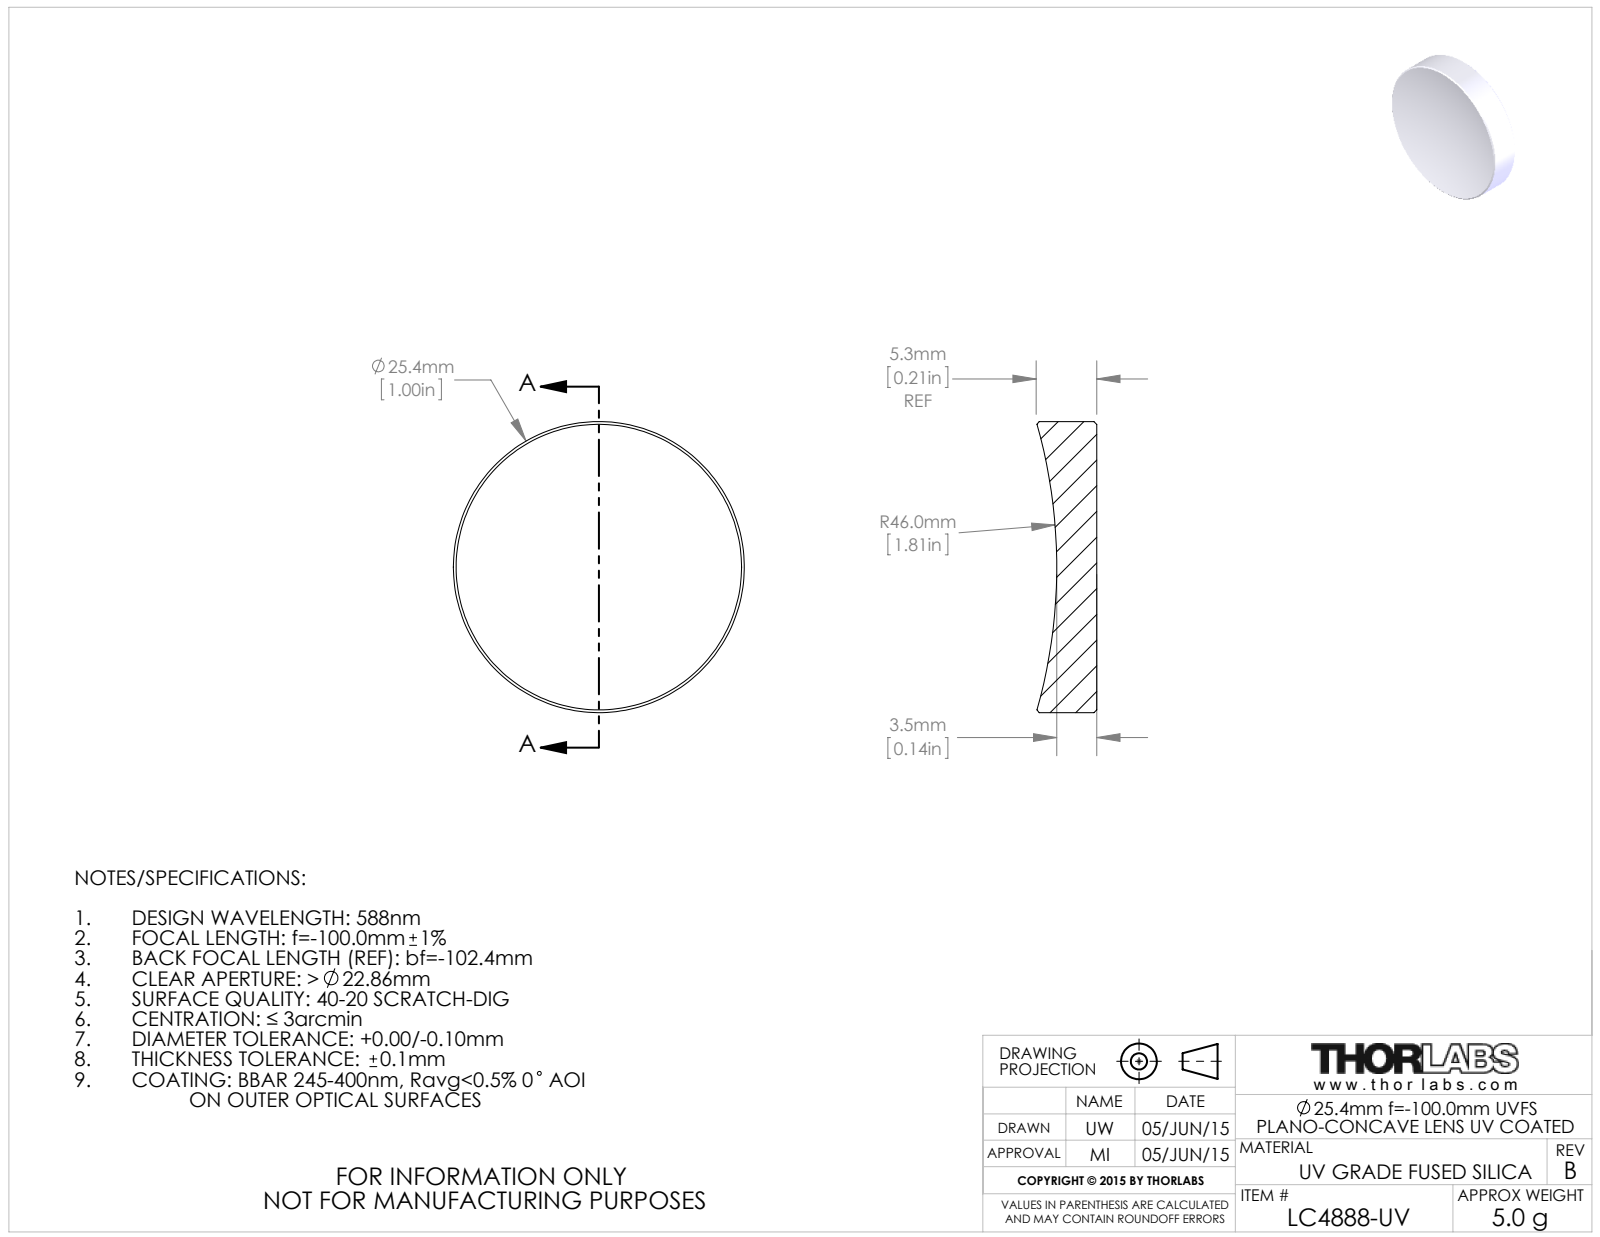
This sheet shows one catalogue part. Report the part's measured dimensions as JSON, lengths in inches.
{"part_name": "4353-E0W", "step_written_by": "SolidWorks 2014 (CONFIG_CONTROL_DESIGN)", "units": "inches", "bodies": {"solids": 1, "faces": 9, "planar": 1, "cylindrical": 2, "other": 6}, "overall_size": [1, 1, 0.206], "volume_in3": 0.135, "surface_area_in2": 2.198, "round_bosses_or_shafts": [[1, 1]]}
